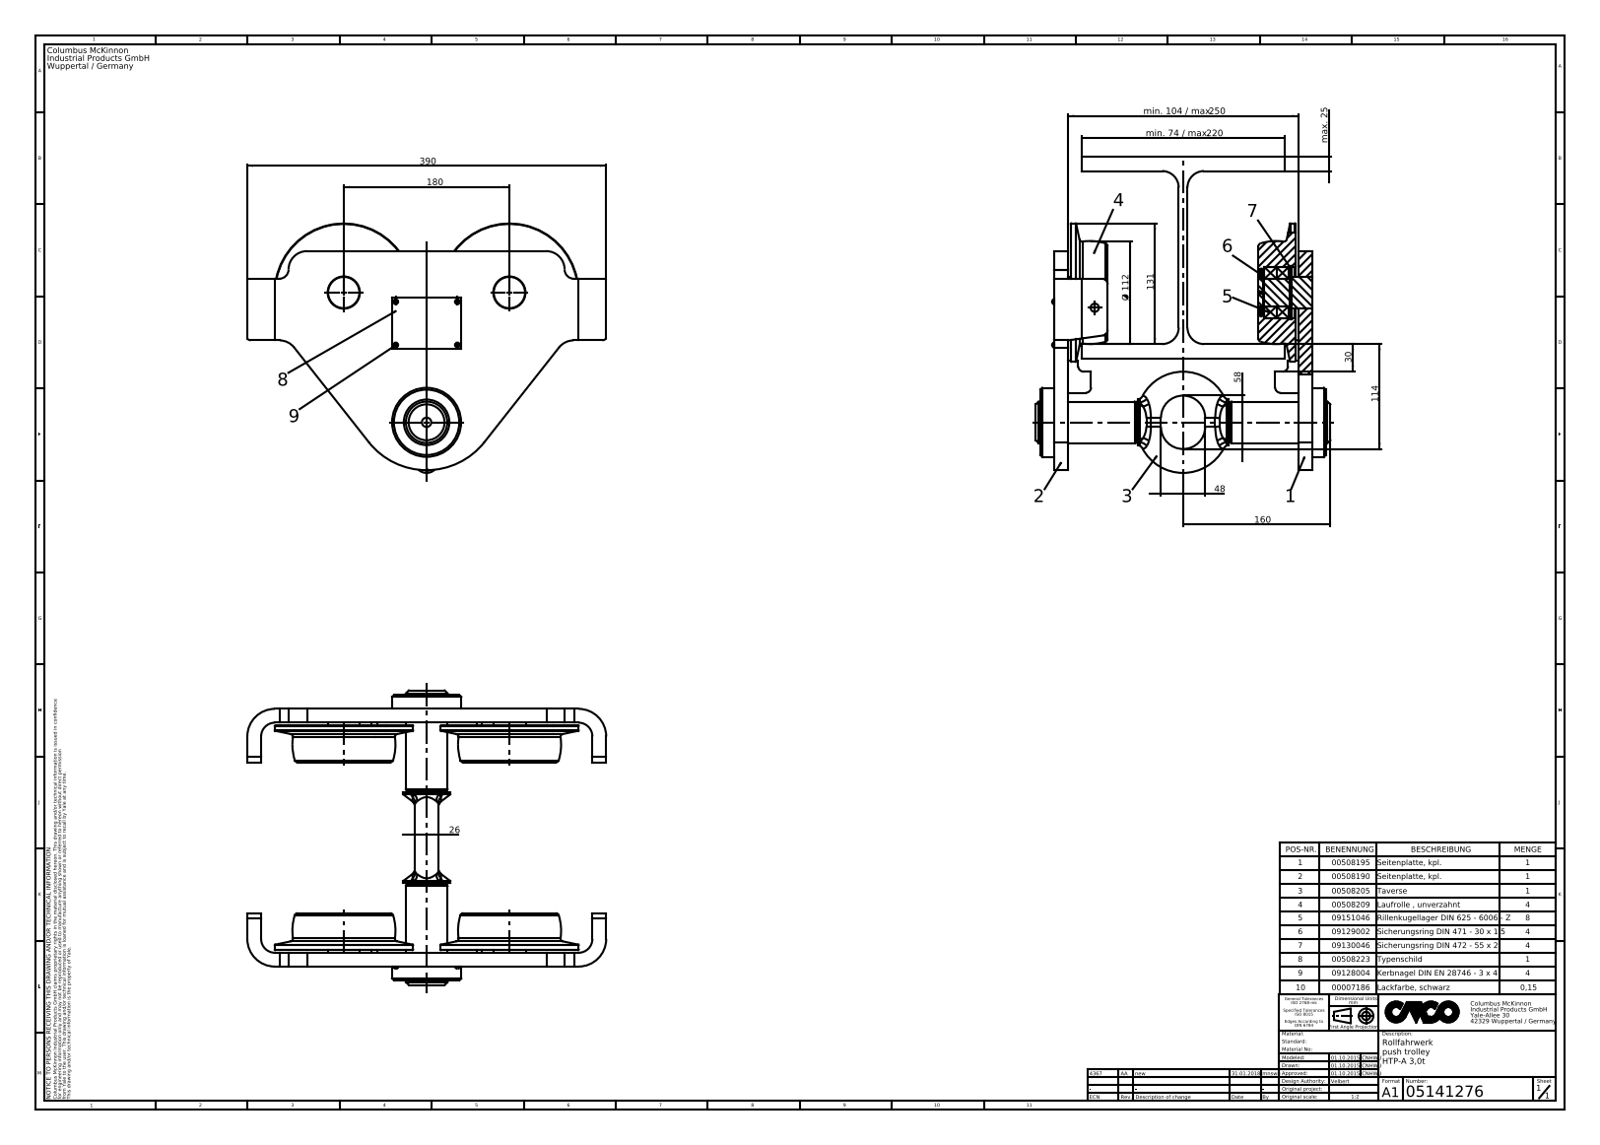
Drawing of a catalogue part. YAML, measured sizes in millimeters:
part_name: "HTP-A 3,0t"
step_written_by: "SolidWorks 2015 (AUTOMOTIVE_DESIGN)"
units: millimeters
bodies: {solids: 39, faces: 890, planar: 246, cylindrical: 352, other: 292}
overall_size: [500, 344, 320]
volume: 8792000
surface_area: 1356000
round_holes:
  - {diameter: 2, count: 10}
  - {diameter: 2.5, count: 4}
  - {diameter: 3, count: 4}
  - {diameter: 3.5, count: 4}
  - {diameter: 9, count: 2}
  - {diameter: 28.6, count: 2}
  - {diameter: 30, count: 2}
  - {diameter: 35, count: 2}
  - {diameter: 44.4, count: 2}
  - {diameter: 48, count: 2}
  - {diameter: 49.5, count: 2}
  - {diameter: 55, count: 2}
round_bosses_or_shafts:
  - {diameter: 5.2, count: 4}
  - {diameter: 150, count: 2}
  - {diameter: 58, count: 2}
  - {diameter: 38.6, count: 2}
  - {diameter: 75, count: 1}
  - {diameter: 62, count: 1}
  - {diameter: 51, count: 1}
  - {diameter: 45, count: 1}
partial_cylinders:
  - {radius: 2, count: 8}
  - {radius: 6, count: 8}
  - {radius: 2.5, count: 4}
  - {radius: 15, count: 4}
  - {radius: 18, count: 4}
  - {radius: 30, count: 4}
  - {radius: 10, count: 2}
  - {radius: 13, count: 2}
face_to_face_distances: [204, 16, 15, 220, 135.25, 144.75, 265, 120.25, 129.75, 188]
hole_center_spacings: [16.8, 180, 5, 8.82, 23.75, 25.6, 127.56, 6.25]
